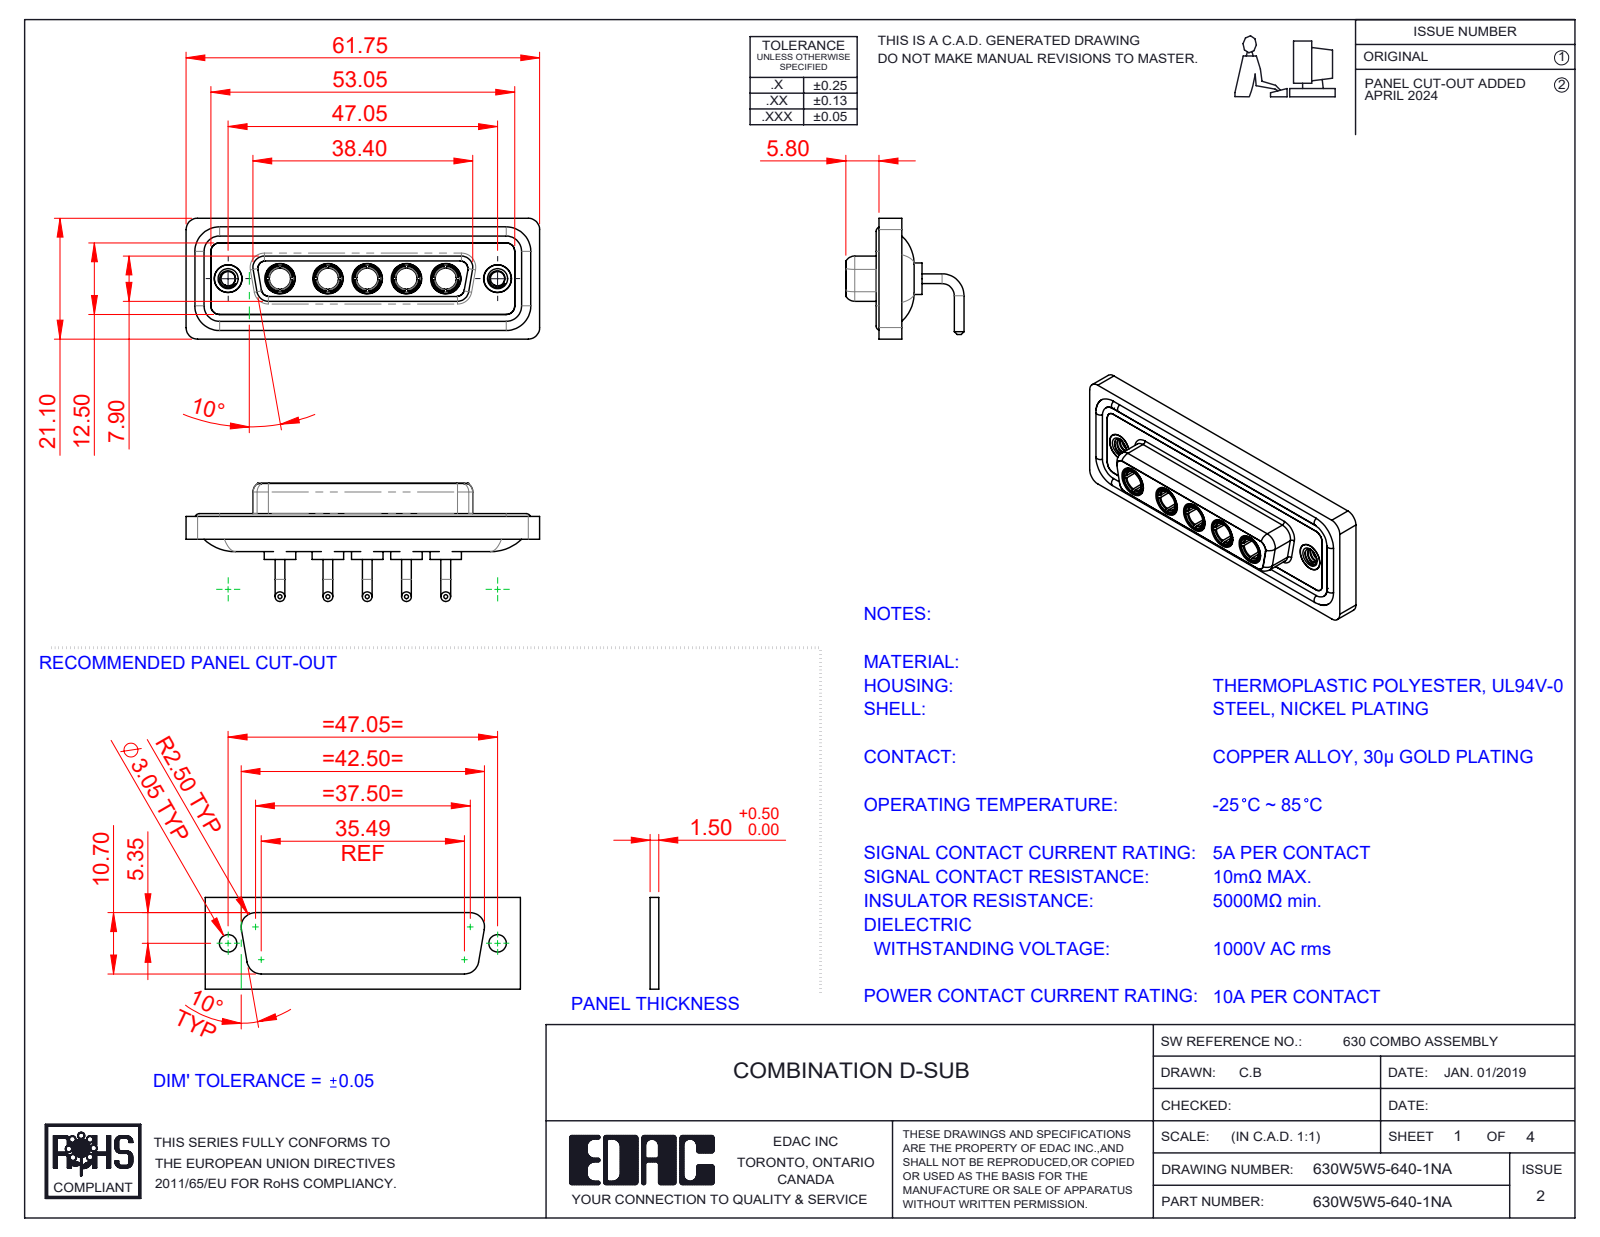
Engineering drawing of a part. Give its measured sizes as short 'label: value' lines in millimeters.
name: 630Combo Threaded Rivet_A; 630Combo Waterproof Housing_25 Contacts; 630W5W5-640-1NA; 630Combo Shell Rear_25 Contacts (+3 more)
written by: SolidWorks 2023 (CONFIG_CONTROL_DESIGN)
unit: mm
bodies: 17 solids, 770 faces (250 planar, 311 cylindrical, 209 other)
size: 61.75 × 21.1 × 20.65
volume: 8 139 mm³; area: 13 563 mm²
holes: 7× ⌀4.85, 5× ⌀3.7, 5× ⌀5.3, 2× ⌀2.5, 2× ⌀4, 2× ⌀4.05, 2× ⌀5
bosses: 10× ⌀1.7, 5× ⌀5.5, 5× ⌀5.2, 5× ⌀4.96, 5× ⌀4.75, 5× ⌀3.75, 4× ⌀1.6, 2× ⌀4.95
rounds: 18× R1.5, 18× R2, 8× R1.35, 8× R1.6, 5× R2.1, 4× R0.25, 4× R0.5, 4× R0.6
face distances: 0.4, 1.8, 4.1, 1.1, 1.5, 2.5, 3.1, 3.7, 1.6, 1.35
hole spacings: 6.86, 9.04, 38.01, 6.87, 8.38, 13.72, 13.73, 15.25
